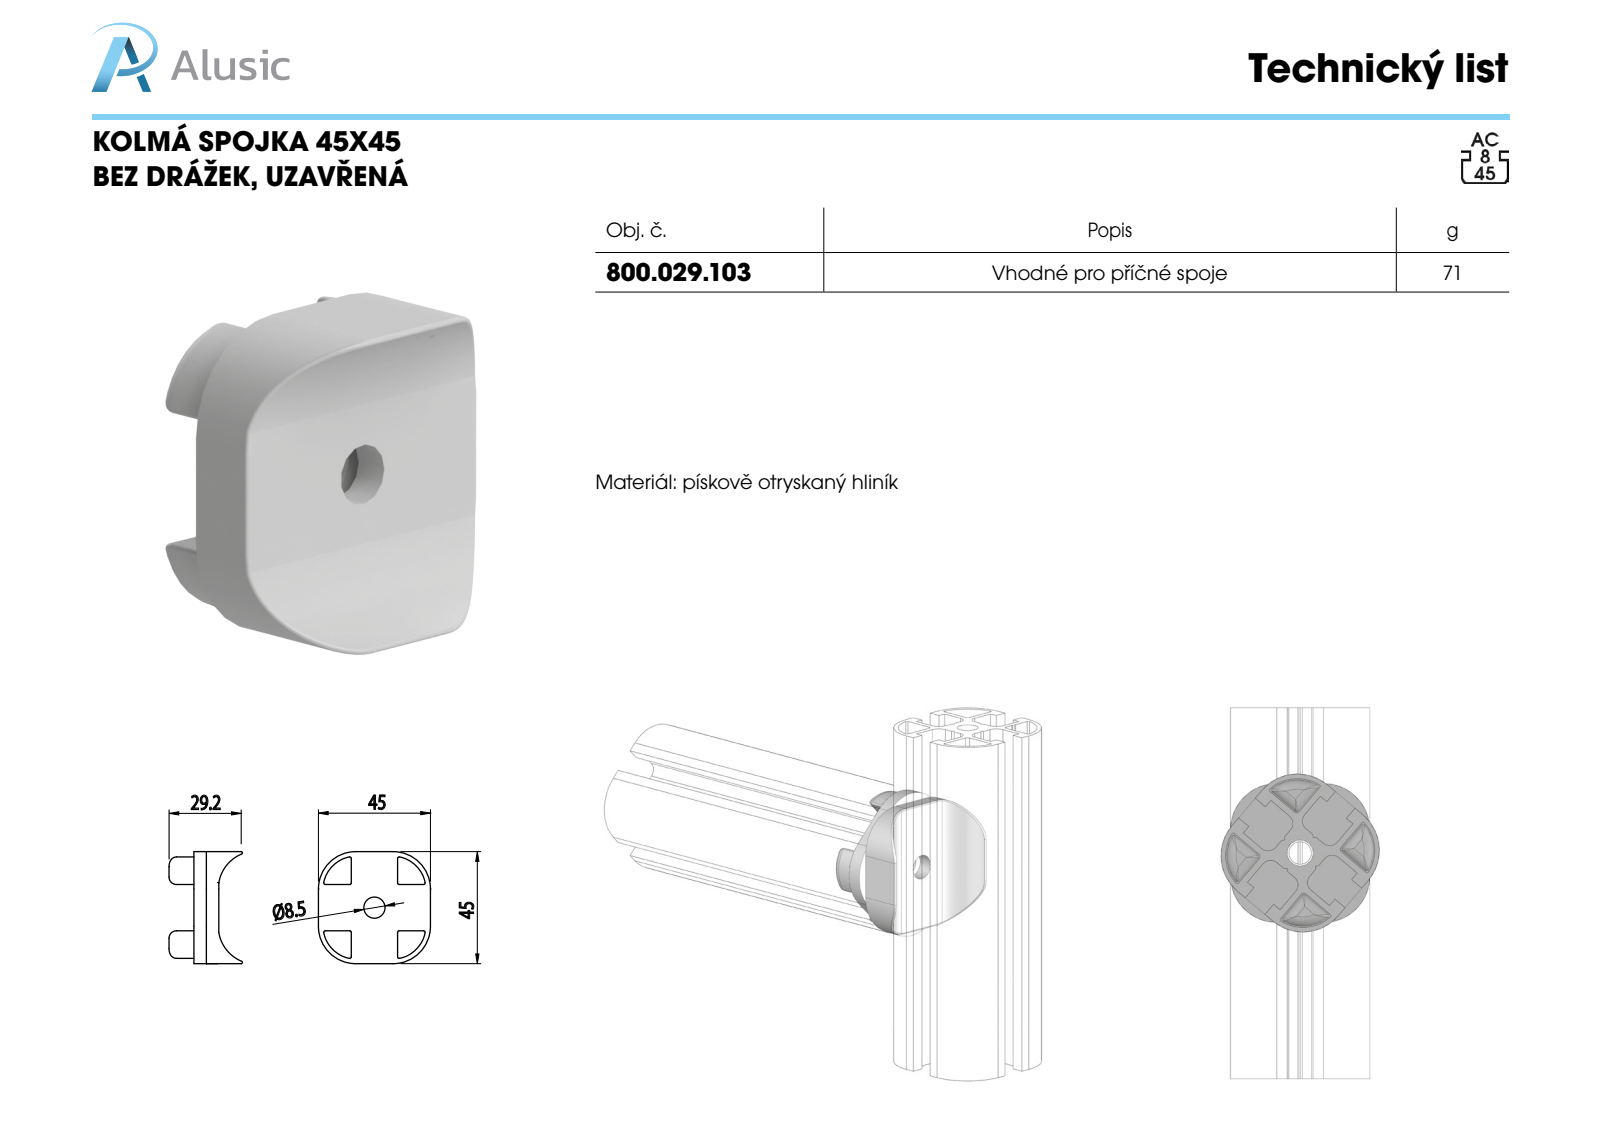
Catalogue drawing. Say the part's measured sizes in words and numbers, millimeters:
The part is named "800.029.103; 800.029.103B; 800.029.103A". Its 3-D file was written by "SolidWorks 2011 (CONFIG_CONTROL_DESIGN)". It is 74 solids with 674 faces: 550 planar, 84 cylindrical and 40 other. Overall it measures 45 by 45 by 29.48 millimeters. Its volume is 23 043 cubic millimeters and its surface area 12 821 square millimeters. Round holes: 1 of diameter 8.5, 1 of diameter 23, 1 of diameter 38. Round bosses or shafts: 1 of diameter 28. Partial cylindrical surfaces (rounded edges, fillets, slot ends): 28 of radius 0.1, 12 of radius 0.6, 4 of radius 0.5, 4 of radius 3, 4 of radius 13.1, 4 of radius 15, 2 of radius 15.2. The main face-to-face distances are 5, 10, 13.2, 31.8, 45, 7, 2, 3, 18.6, 13.5.
